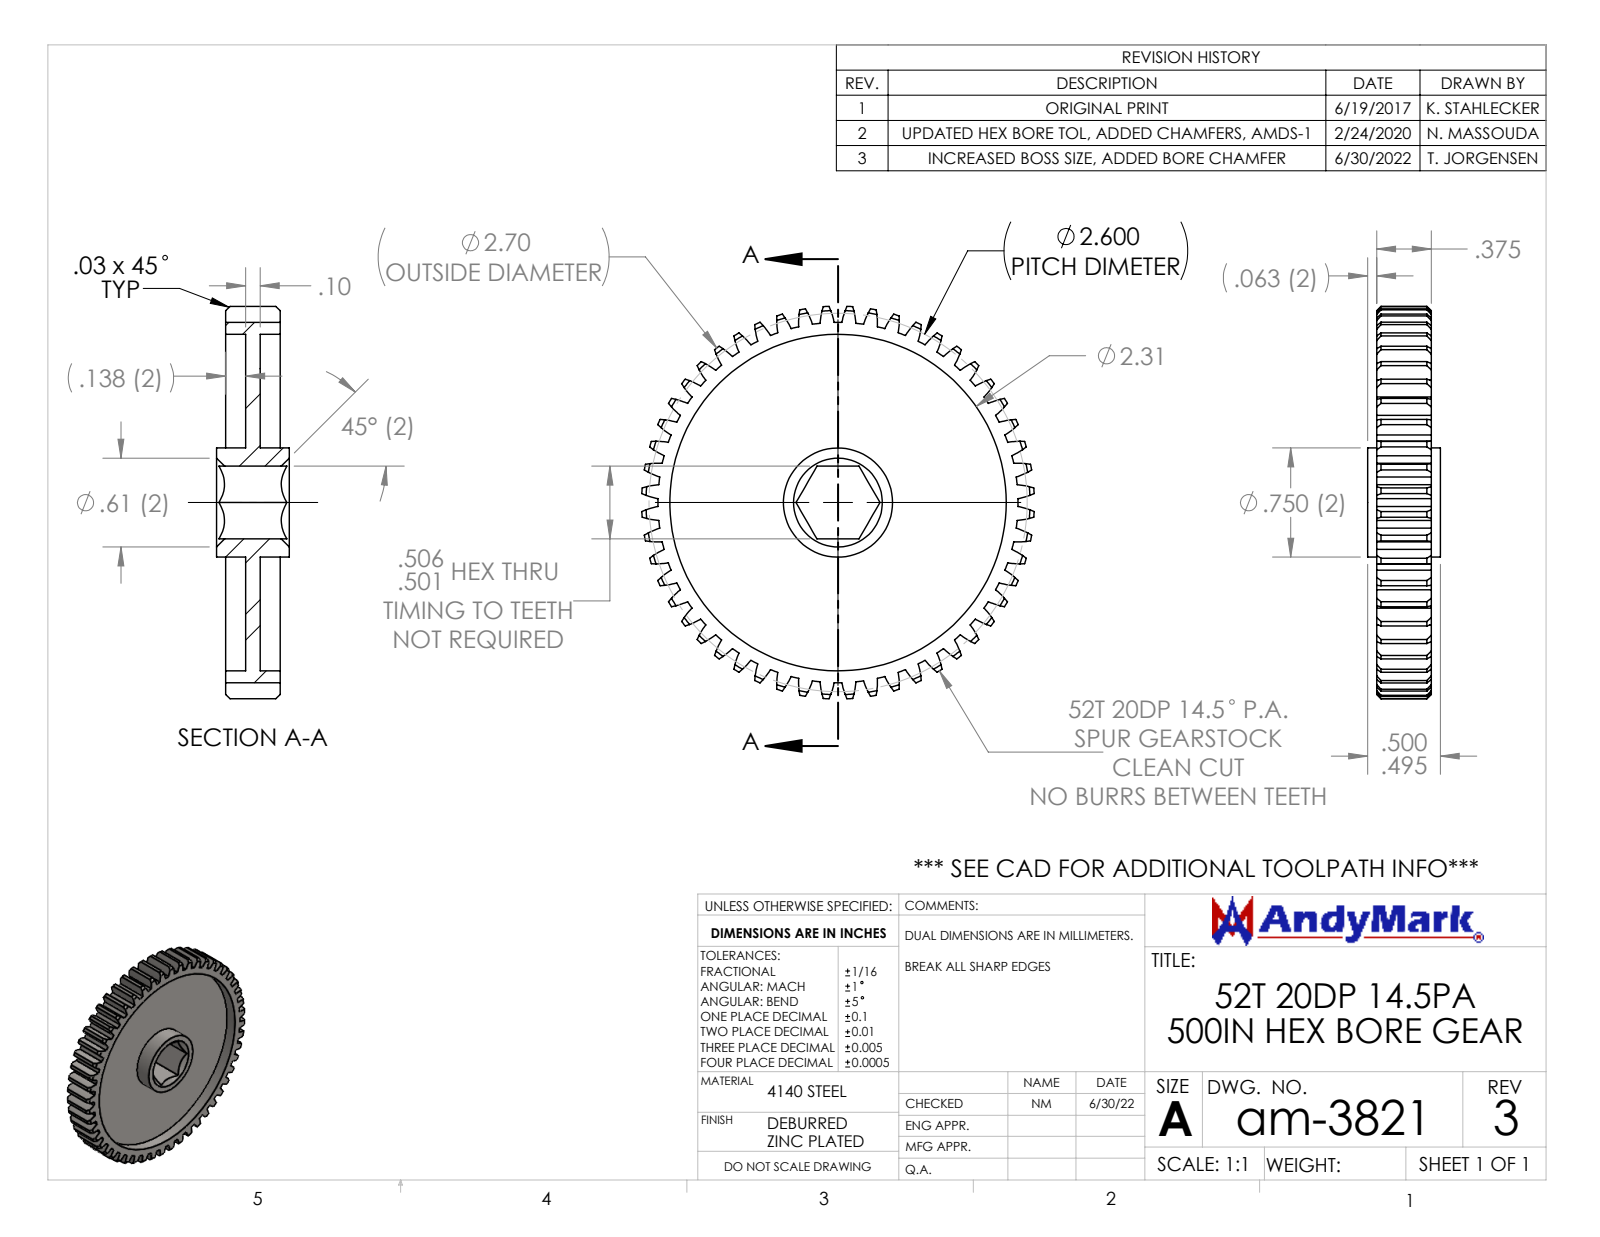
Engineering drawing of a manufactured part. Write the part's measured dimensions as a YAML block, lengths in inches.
part_name: "am-3821 52T 20DP 500hex 375 FW"
step_written_by: "SolidWorks 2022 (CONFIG_CONTROL_DESIGN)"
units: inches
bodies: {solids: 1, faces: 341, planar: 12, cylindrical: 221, other: 108}
overall_size: [2.697, 2.697, 0.5]
volume: 0.872
surface_area: 19.97
round_holes:
  - {diameter: 2.313, count: 1}
round_bosses_or_shafts:
  - {diameter: 0.75, count: 1}
partial_cylinders:
  - {radius: 0.52, count: 104}
  - {radius: 1.238, count: 1}
  - {radius: 1.35, count: 1}
face_to_face_distances: [0.1, 0.137, 0.237, 0.375, 0.238, 0.138, 0.5, 0.2, 0.3, 0.063]
